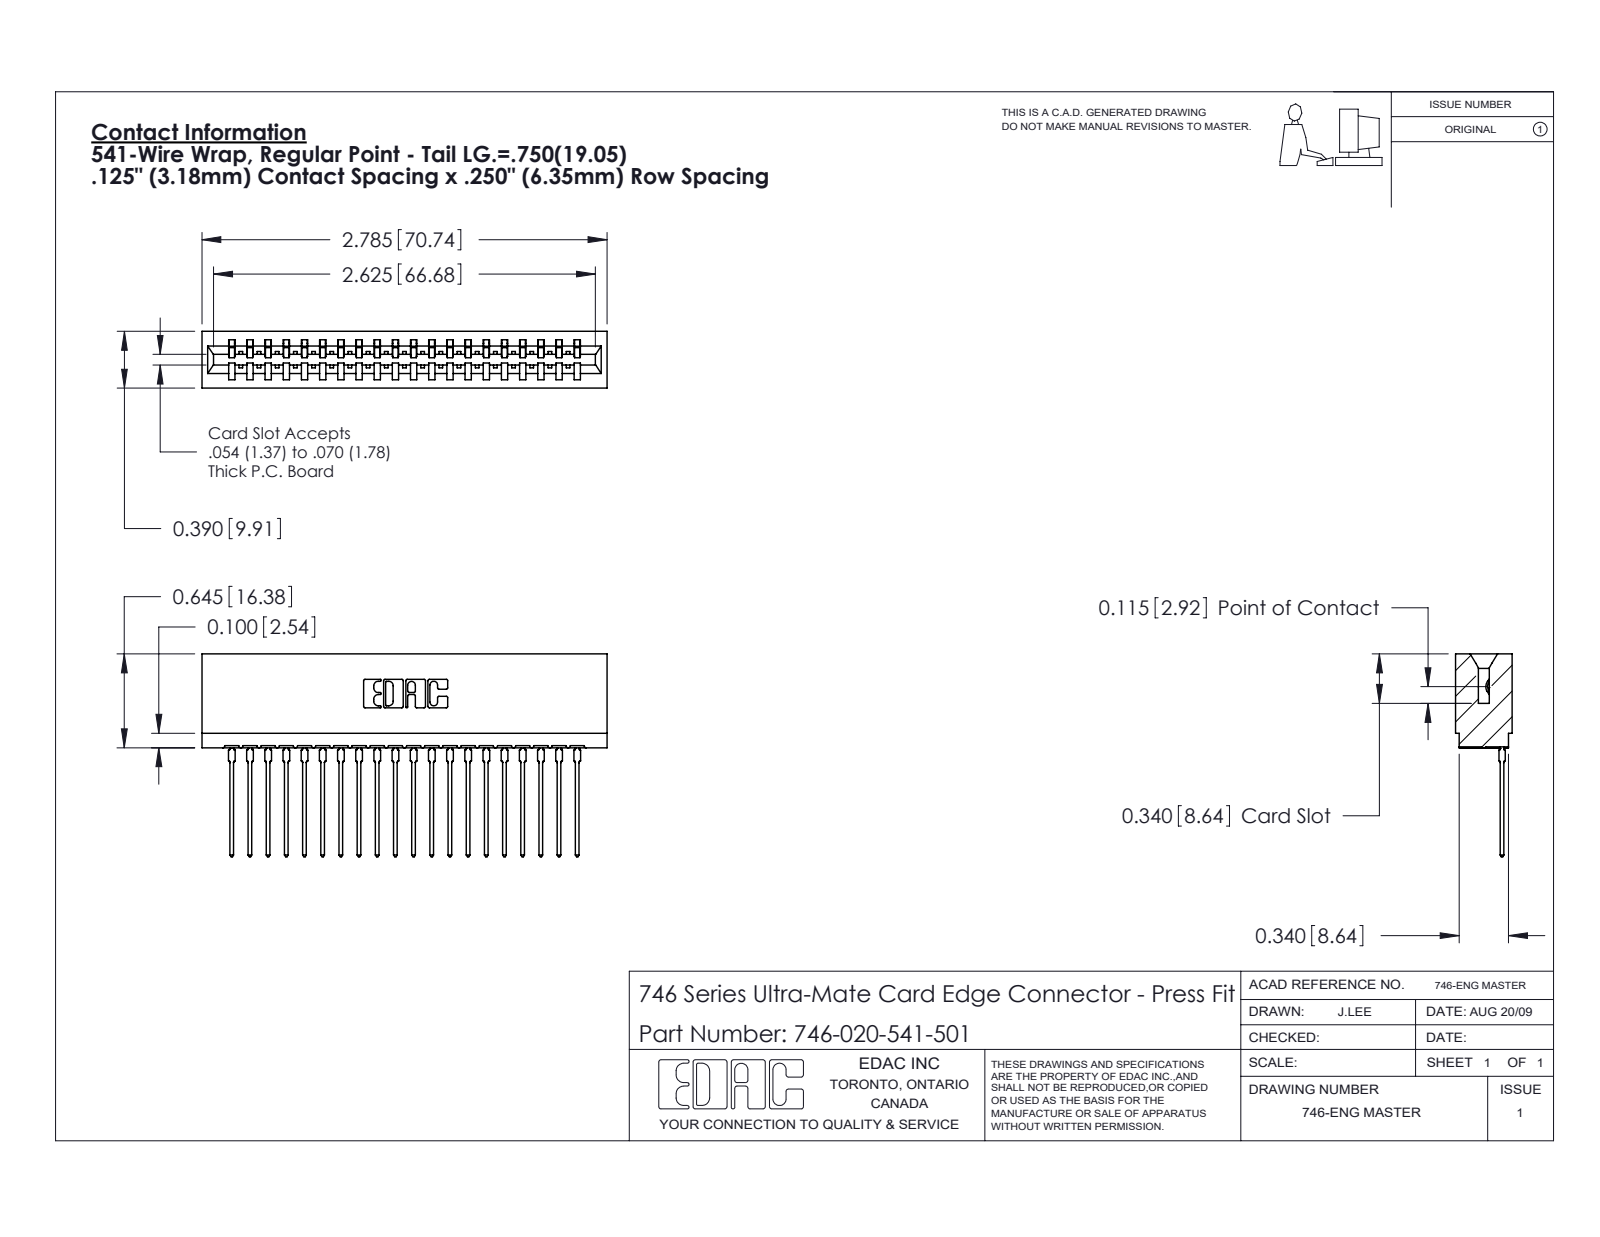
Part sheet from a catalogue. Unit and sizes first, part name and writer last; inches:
Units: inches
Overall size (bounding box): 2.785 × 1.394 × 0.39
Partial cylindrical surfaces — rounded edges, fillets, slot ends (radius × count): R0.021 ×40, R0.01 ×22, R0.015 ×21, R0.007 ×6, R0.031 ×6, R0.005 ×4, R0.011 ×4, R0.026 ×3
Main face-to-face distances: 0.25, 0.057, 0.333, 0.39, 0.5, 0.025, 0.307, 0.125, 0.292, 0.125
Volume: 0.499 in³ · Surface area: 17.32 in²
Bodies: 21 solids, 2257 faces (1315 planar, 422 cylindrical, 520 other)
Part name (STEP PRODUCT): 746 Part_.340 Slot Depth - 01; 746-020-541-501; 746-292-001_541
STEP written by: SolidWorks 2020 (CONFIG_CONTROL_DESIGN)
